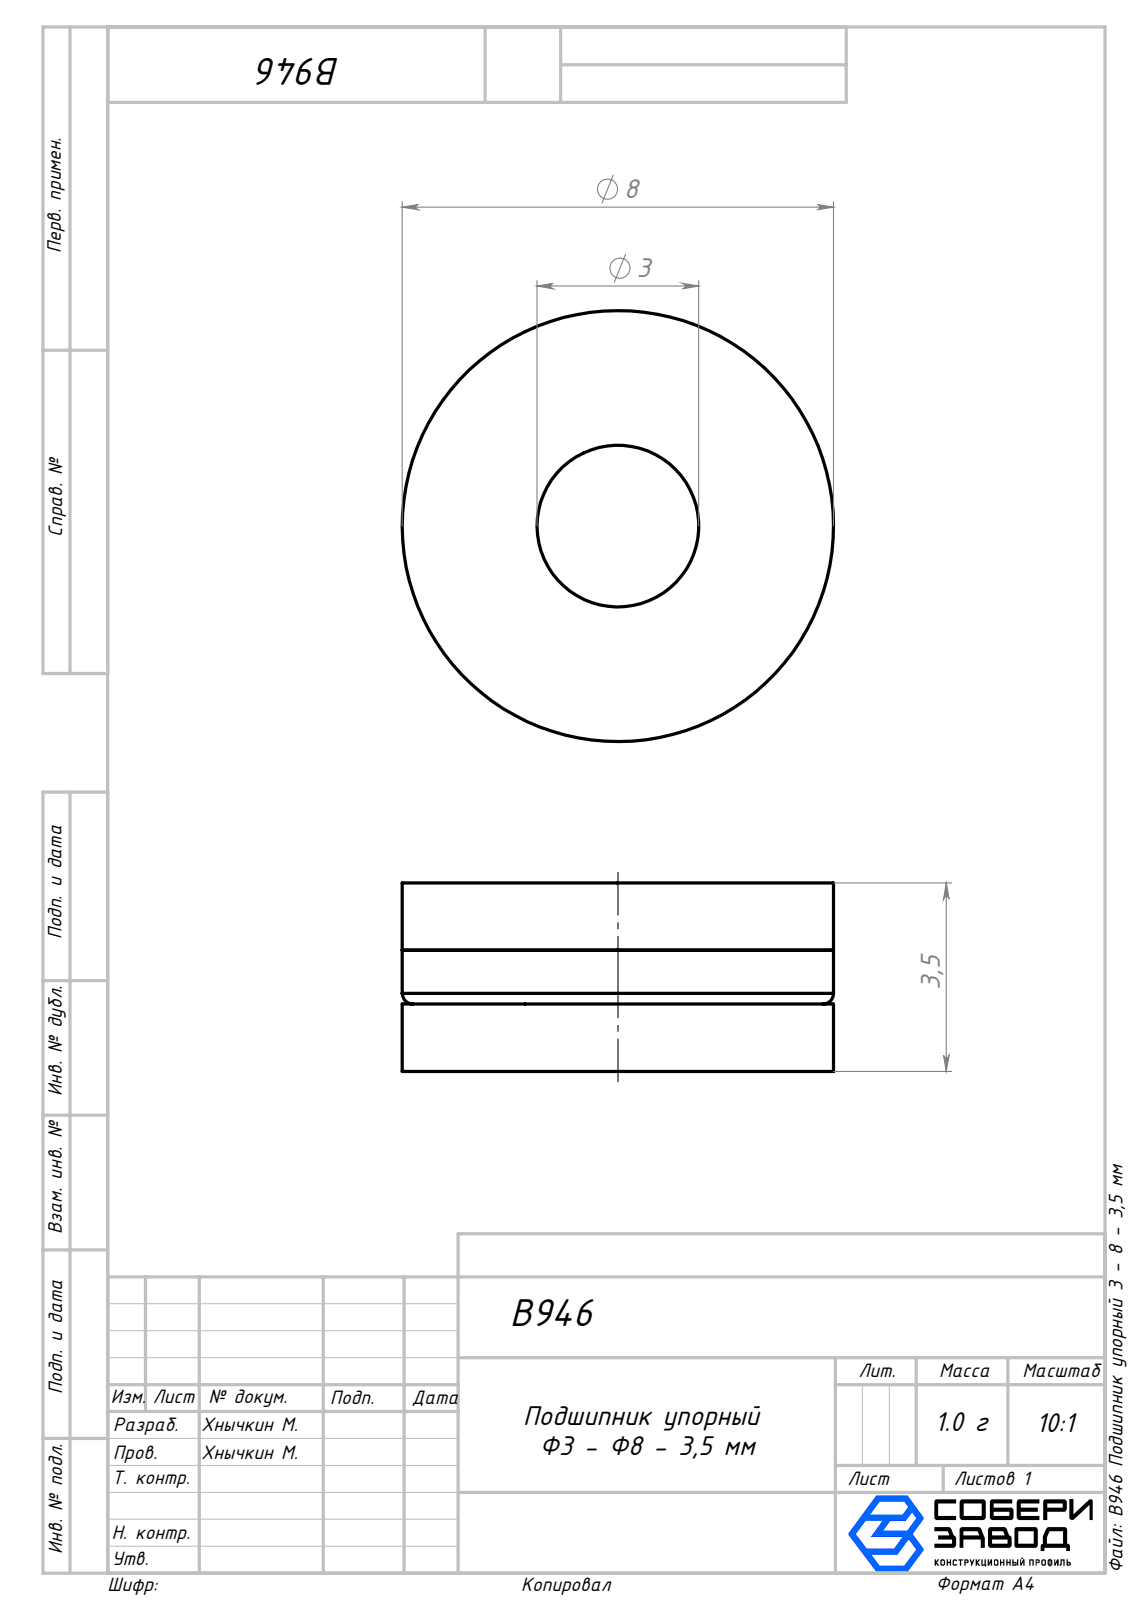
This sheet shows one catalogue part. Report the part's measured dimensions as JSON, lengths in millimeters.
{"part_name": "B946 Шарик_00; B946 Первая часть_00; B946 Внутренняя часть_00; B946 Подшипник упорный 3 - 8 - 3,5 мм", "step_written_by": "SolidWorks 2026 (AUTOMOTIVE_DESIGN)", "units": "millimeters", "bodies": {"solids": 12, "faces": 74, "planar": 12, "cylindrical": 34, "other": 28}, "overall_size": [8, 8, 3.5], "volume_mm3": 121, "surface_area_mm2": 440, "round_holes": [[1.2, 9], [3, 1], [7.6, 1]], "round_bosses_or_shafts": [[8, 1], [3.4, 1]], "face_to_face_distances": [1.25, 2.25, 3.5, 1, 1.35, 0.9, 2.15, 1.05, 2.45, 1.2], "hole_center_spacings": [2.75, 1.88, 5.42, 3.54, 4.76, 3.53, 4.77, 5.41]}
